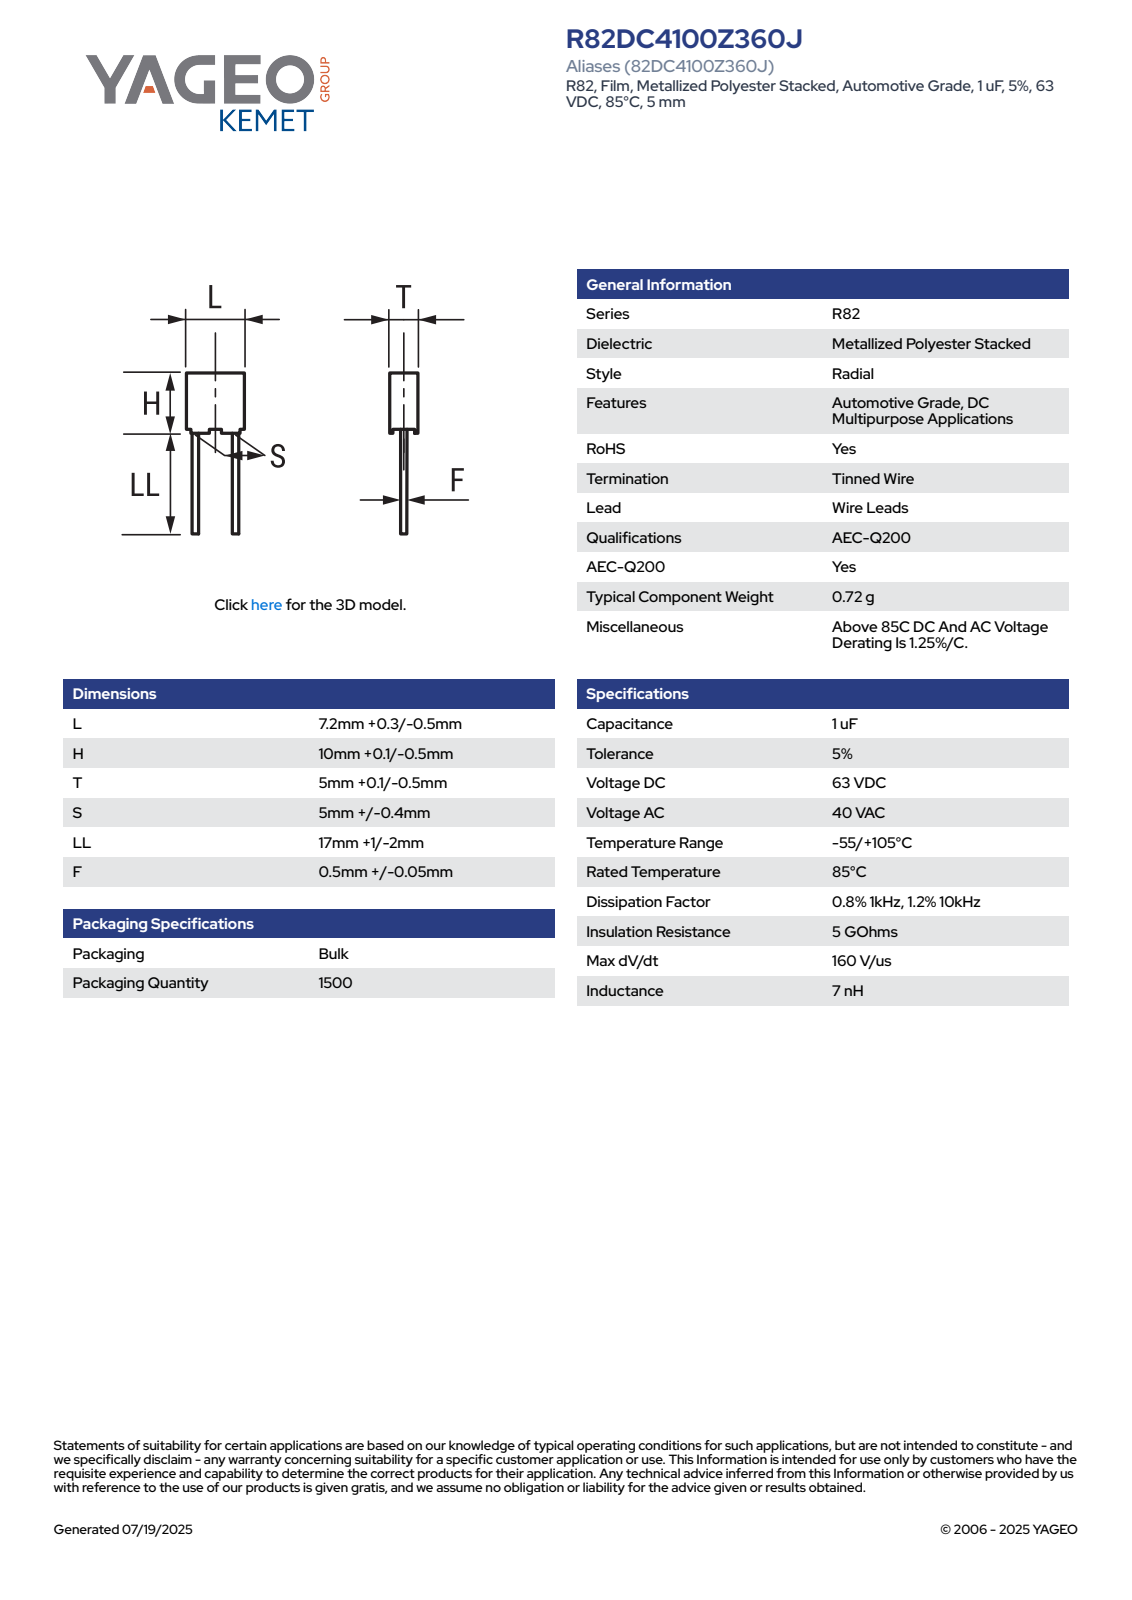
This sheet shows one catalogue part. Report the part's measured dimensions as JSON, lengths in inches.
{"part_name": "CFR_RB3_7.2X10X5_L7.5H10.1T5.1S5LL18F0.55", "step_written_by": "SolidWorks 2014 (AUTOMOTIVE_DESIGN)", "units": "inches", "bodies": {"solids": 4, "faces": 85, "planar": 77, "cylindrical": 8, "other": 0}, "overall_size": [1.106, 0.295, 0.201], "volume_in3": 0.023, "surface_area_in2": 0.636, "round_bosses_or_shafts": [[0.022, 2]], "partial_cylinders_radius": [[0.02, 4]], "face_to_face_distances": [0.201, 0.295, 0.368, 0.191, 0.285, 0.03, 0.398, 0.181, 0.276, 0.014]}
